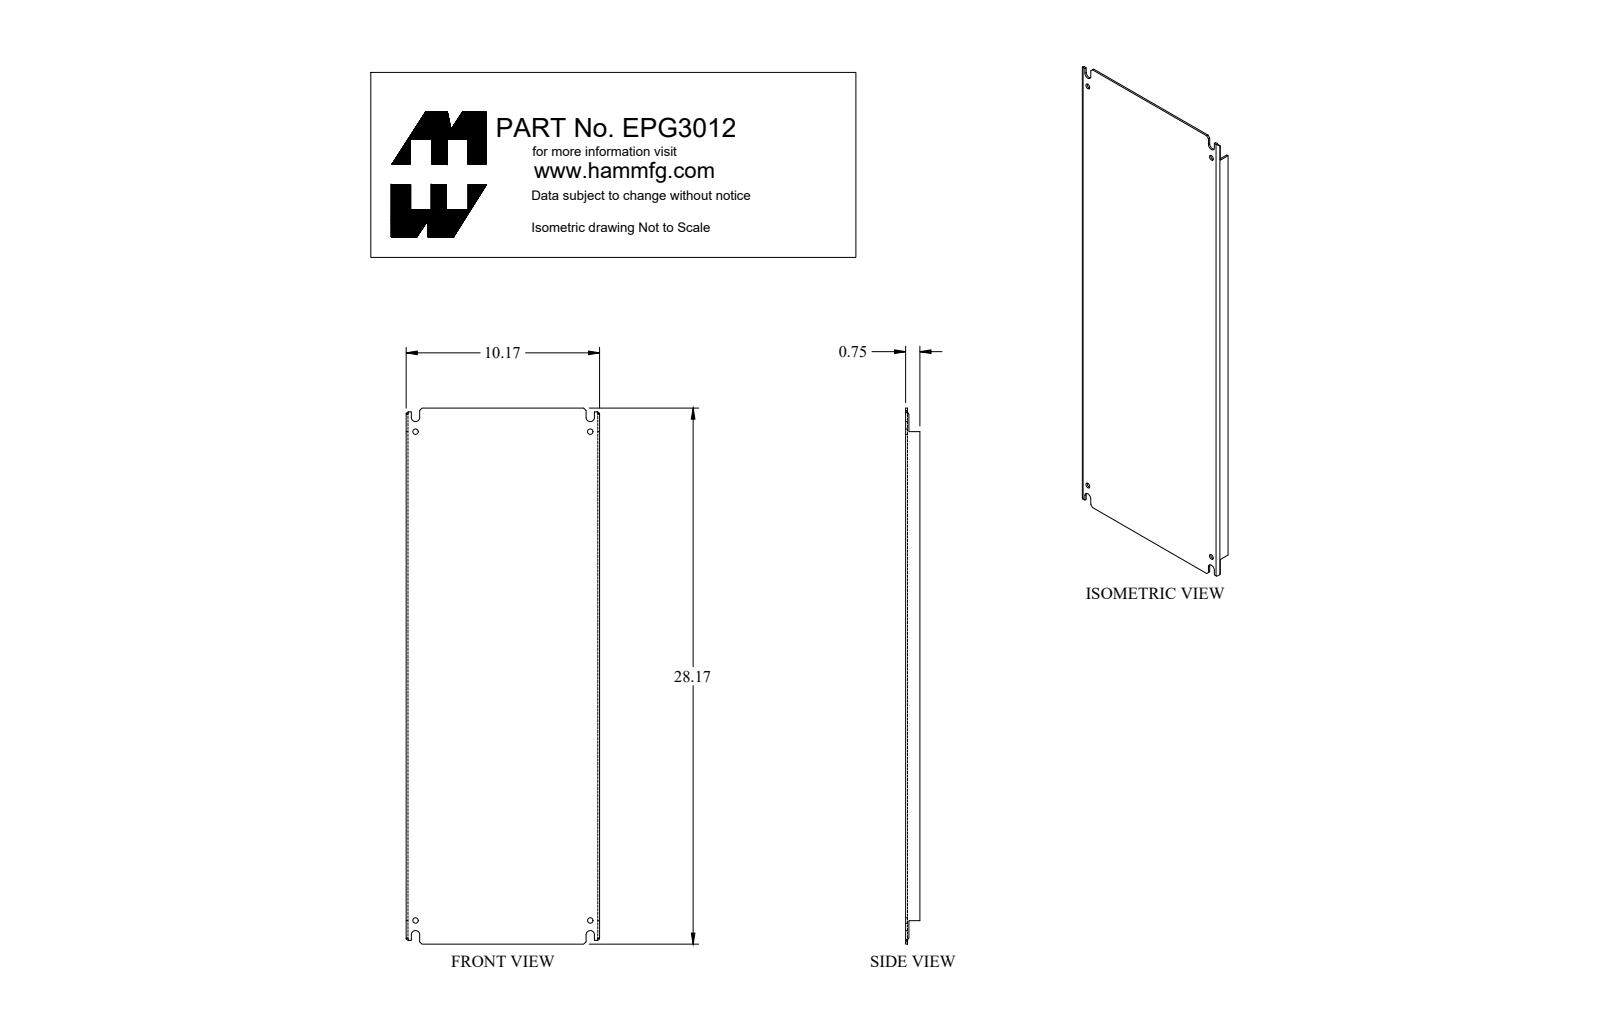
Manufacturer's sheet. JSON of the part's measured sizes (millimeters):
{"part_name": "EPG3012", "step_written_by": "SolidWorks 2018 (AUTOMOTIVE_DESIGN)", "units": "millimeters", "bodies": {"solids": 1, "faces": 84, "planar": 50, "cylindrical": 26, "other": 8}, "overall_size": [715.5, 258.3, 19.1], "volume_mm3": 492600, "surface_area_mm2": 413500, "round_holes": [[7.1, 4]], "partial_cylinders_radius": [[5.6, 4], [1.2, 2], [1.6, 2], [3.6, 2]], "face_to_face_distances": [2.4, 255.9, 253.5, 258.3, 19.1, 16.6, 715.5, 4.3, 1.9, 14.7], "hole_center_spacings": [233.4, 652.5, 693]}
